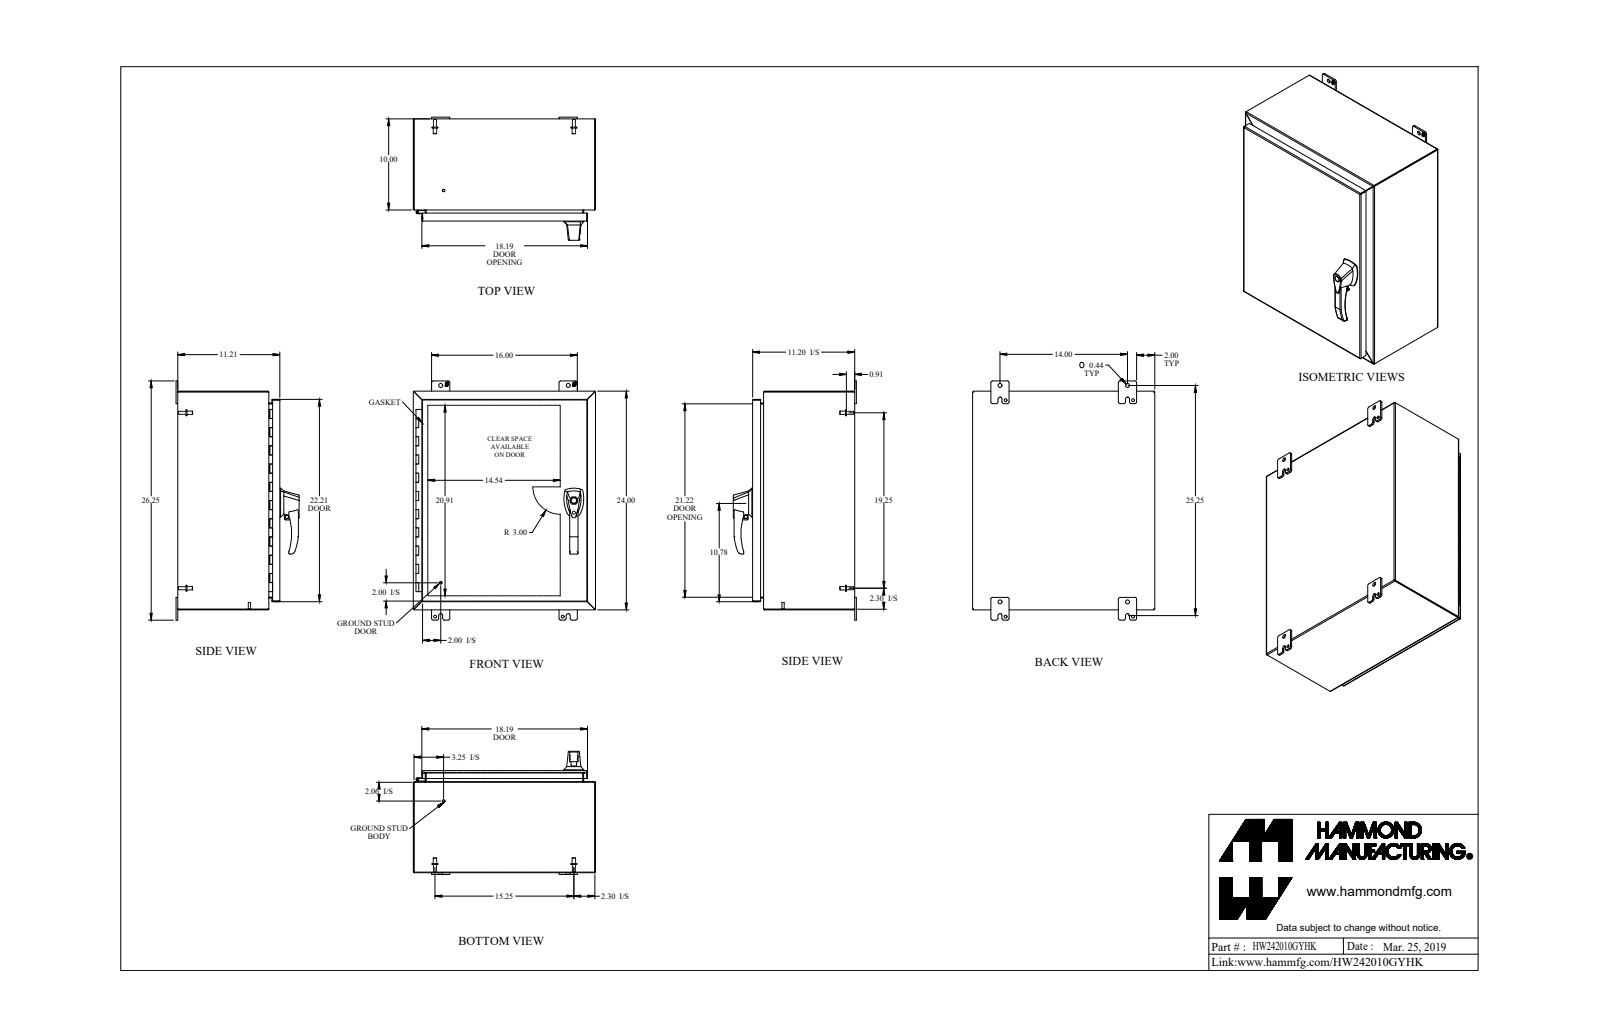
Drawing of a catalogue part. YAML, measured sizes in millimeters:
part_name: "HW242010GYHK"
step_written_by: "SolidWorks 2018 (AUTOMOTIVE_DESIGN)"
units: millimeters
bodies: {solids: 41, faces: 1404, planar: 691, cylindrical: 555, other: 158}
overall_size: [666.8, 508, 343.2]
volume: 2971000
surface_area: 2964000
round_holes:
  - {diameter: 4.5, count: 6}
  - {diameter: 6.4, count: 4}
  - {diameter: 8, count: 4}
  - {diameter: 5, count: 3}
  - {diameter: 6.7, count: 3}
  - {diameter: 10.5, count: 3}
  - {diameter: 6.5, count: 2}
  - {diameter: 10, count: 2}
  - {diameter: 11.1, count: 2}
  - {diameter: 4.7, count: 1}
  - {diameter: 5.9, count: 1}
  - {diameter: 8.5, count: 1}
round_bosses_or_shafts:
  - {diameter: 9.5, count: 9}
  - {diameter: 6.4, count: 6}
  - {diameter: 4, count: 6}
  - {diameter: 16.5, count: 4}
  - {diameter: 8.4, count: 4}
  - {diameter: 25.4, count: 3}
  - {diameter: 16, count: 2}
  - {diameter: 13, count: 2}
partial_cylinders:
  - {radius: 6.4, count: 27}
  - {radius: 4.8, count: 24}
  - {radius: 0.9, count: 20}
  - {radius: 2.7, count: 20}
  - {radius: 1.5, count: 12}
  - {radius: 3.2, count: 9}
  - {radius: 1.1, count: 8}
  - {radius: 5.5, count: 8}
face_to_face_distances: [1.8, 506.2, 282.9, 281.1, 1.8, 284.7, 282.9, 607.8, 504.3, 508]
hole_center_spacings: [206.2, 206.2, 412.4, 28.2, 199.4, 206.2, 240.2, 355.6]
